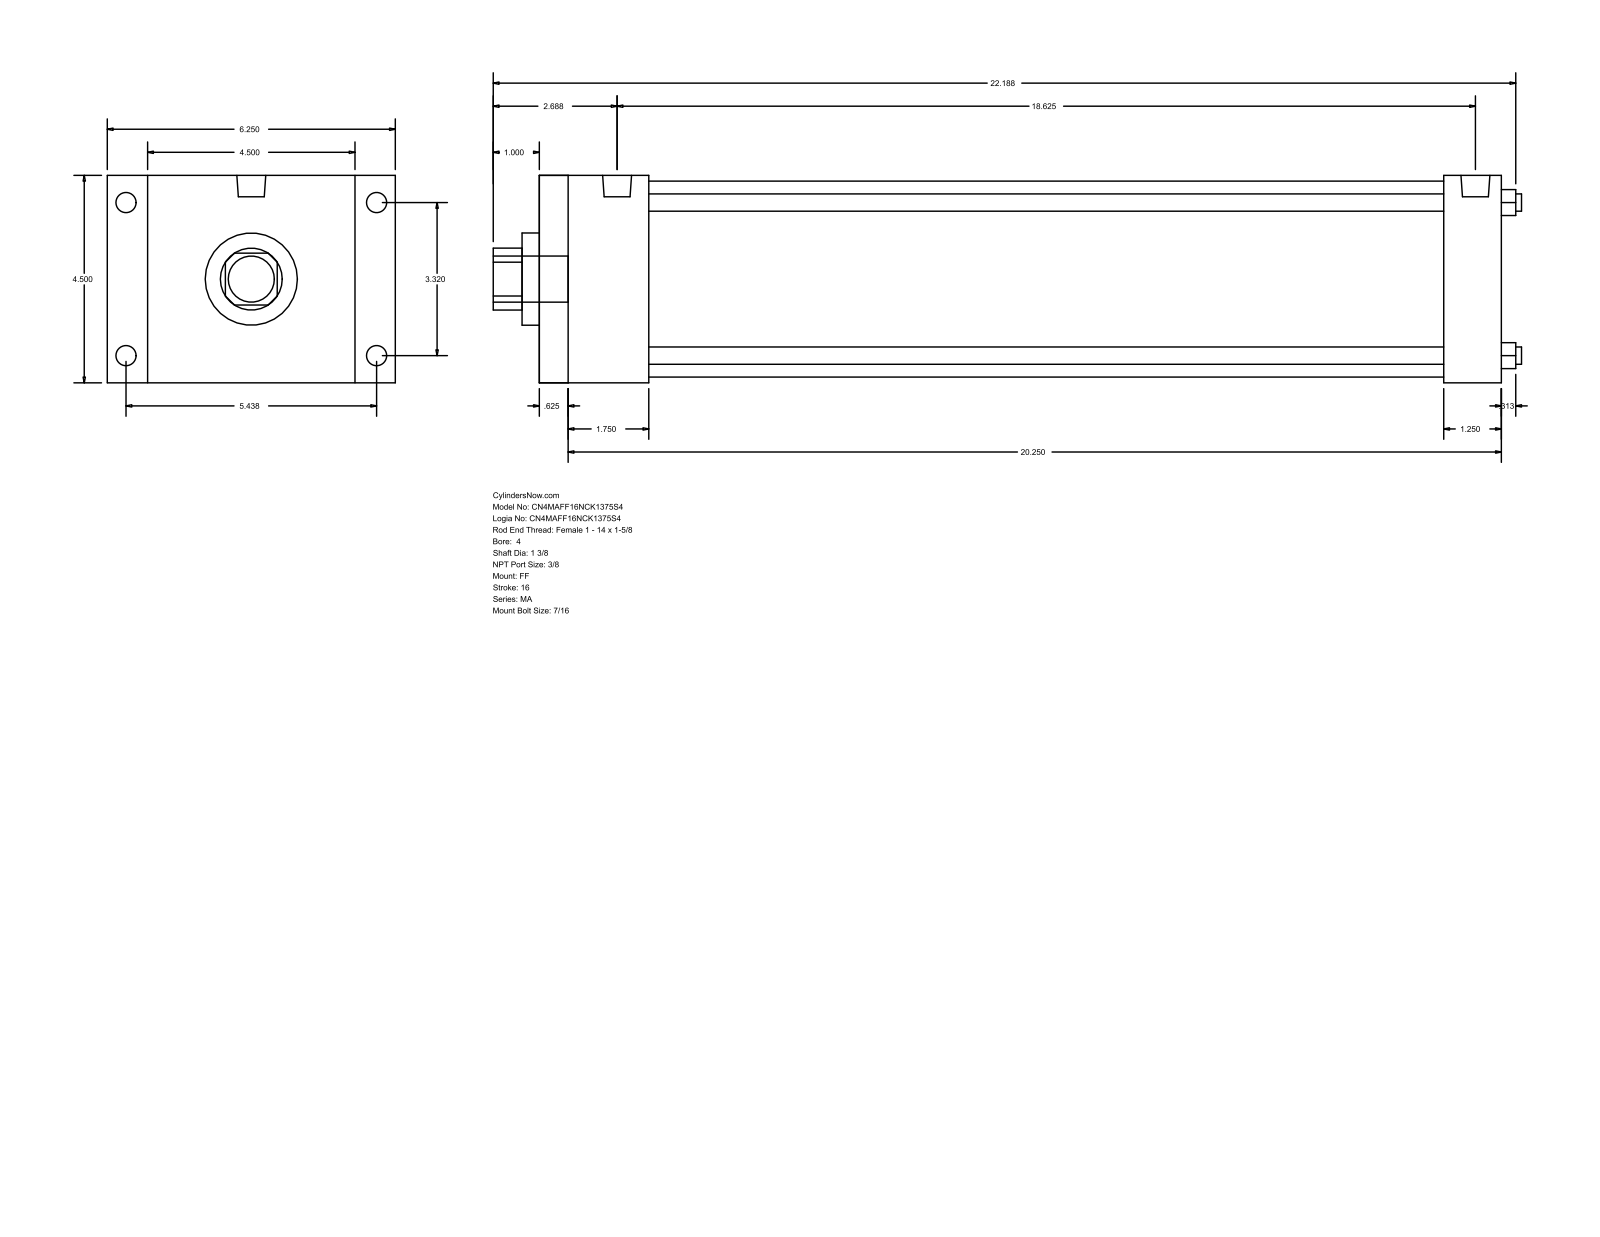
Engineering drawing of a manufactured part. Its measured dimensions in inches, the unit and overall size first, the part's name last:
Units: inches
Overall size (bounding box): 22.313 × 6.25 × 4.5
Round holes (diameter × count): ⌀0.375 ×4, ⌀1.375 ×1, ⌀2 ×1, ⌀4.25 ×1
Round bosses / shafts (diameter × count): ⌀0.437 ×8, ⌀0.627 ×2, ⌀1 ×1
Partial cylindrical surfaces — rounded edges, fillets, slot ends (radius × count): R0.672 ×1
Main face-to-face distances: 4.5, 20.875, 0.625, 20.25, 0.875, 5.375, 19.625, 19, 1.25, 2.375
Hole centre spacings: 2.347, 3.32, 4.695
Bodies: 0 solids, 92 faces (64 planar, 28 cylindrical, 0 other)
Part name (STEP PRODUCT): MA_FF__0400_1.375
STEP written by: GSSL Pune (CONFIG_CONTROL_DESIGN)
